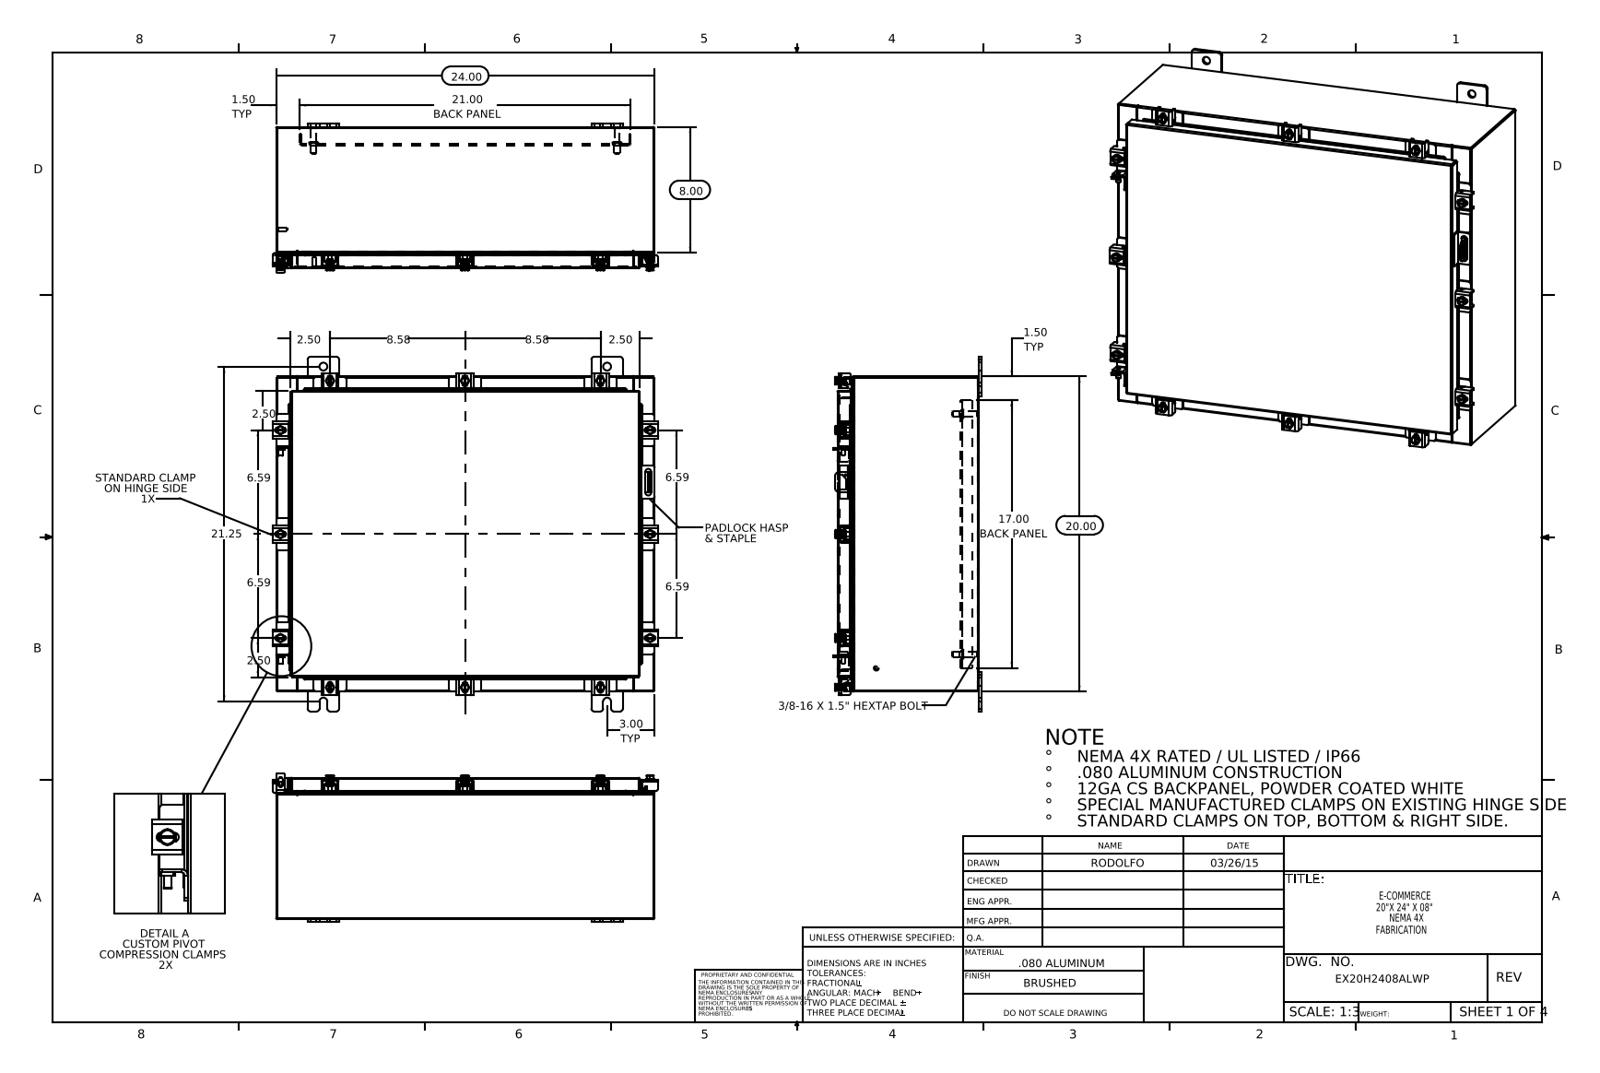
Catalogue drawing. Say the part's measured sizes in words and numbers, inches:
The part is named "EX20H2408ALWP Special Clamp; EX20H2408ALWP Clamp Bracket; EX20H2408ALWP Padlock Staple; Special Clamp Assembly (+8 more)". Its 3-D file was written by "SolidWorks 2014 (CONFIG_CONTROL_DESIGN)". It is 81 solids with 2018 faces: 1075 planar, 783 cylindrical and 160 other. Overall it measures 24.421 by 22.5 by 9.453 inches. Its volume is 186.7 cubic inches and its surface area 4 676 square inches. Round holes: 12 of diameter 0.213, 12 of diameter 0.26, 8 of diameter 0.5, 1 of diameter 0.125, 1 of diameter 0.25. Round bosses or shafts: 12 of diameter 0.5, 12 of diameter 0.25, 10 of diameter 0.399, 4 of diameter 0.625, 4 of diameter 0.375, 4 of diameter 0.33, 2 of diameter 0.315, 2 of diameter 0.236. Partial cylindrical surfaces (rounded edges, fillets, slot ends): 54 of radius 0.06, 24 of radius 0.013, 24 of radius 0.141, 24 of radius 0.19, 22 of radius 0.088, 22 of radius 0.12, 18 of radius 0.09, 17 of radius 0.05. The main face-to-face distances are 0.075, 8.9, 8.975, 8.826, 19.925, 0.104, 1, 1.075, 7.826, 7.9. The hole center spacings are 2.347, 4.44, 6.594, 10.222, 14.373, 16.62, 17.382, 20.544.
